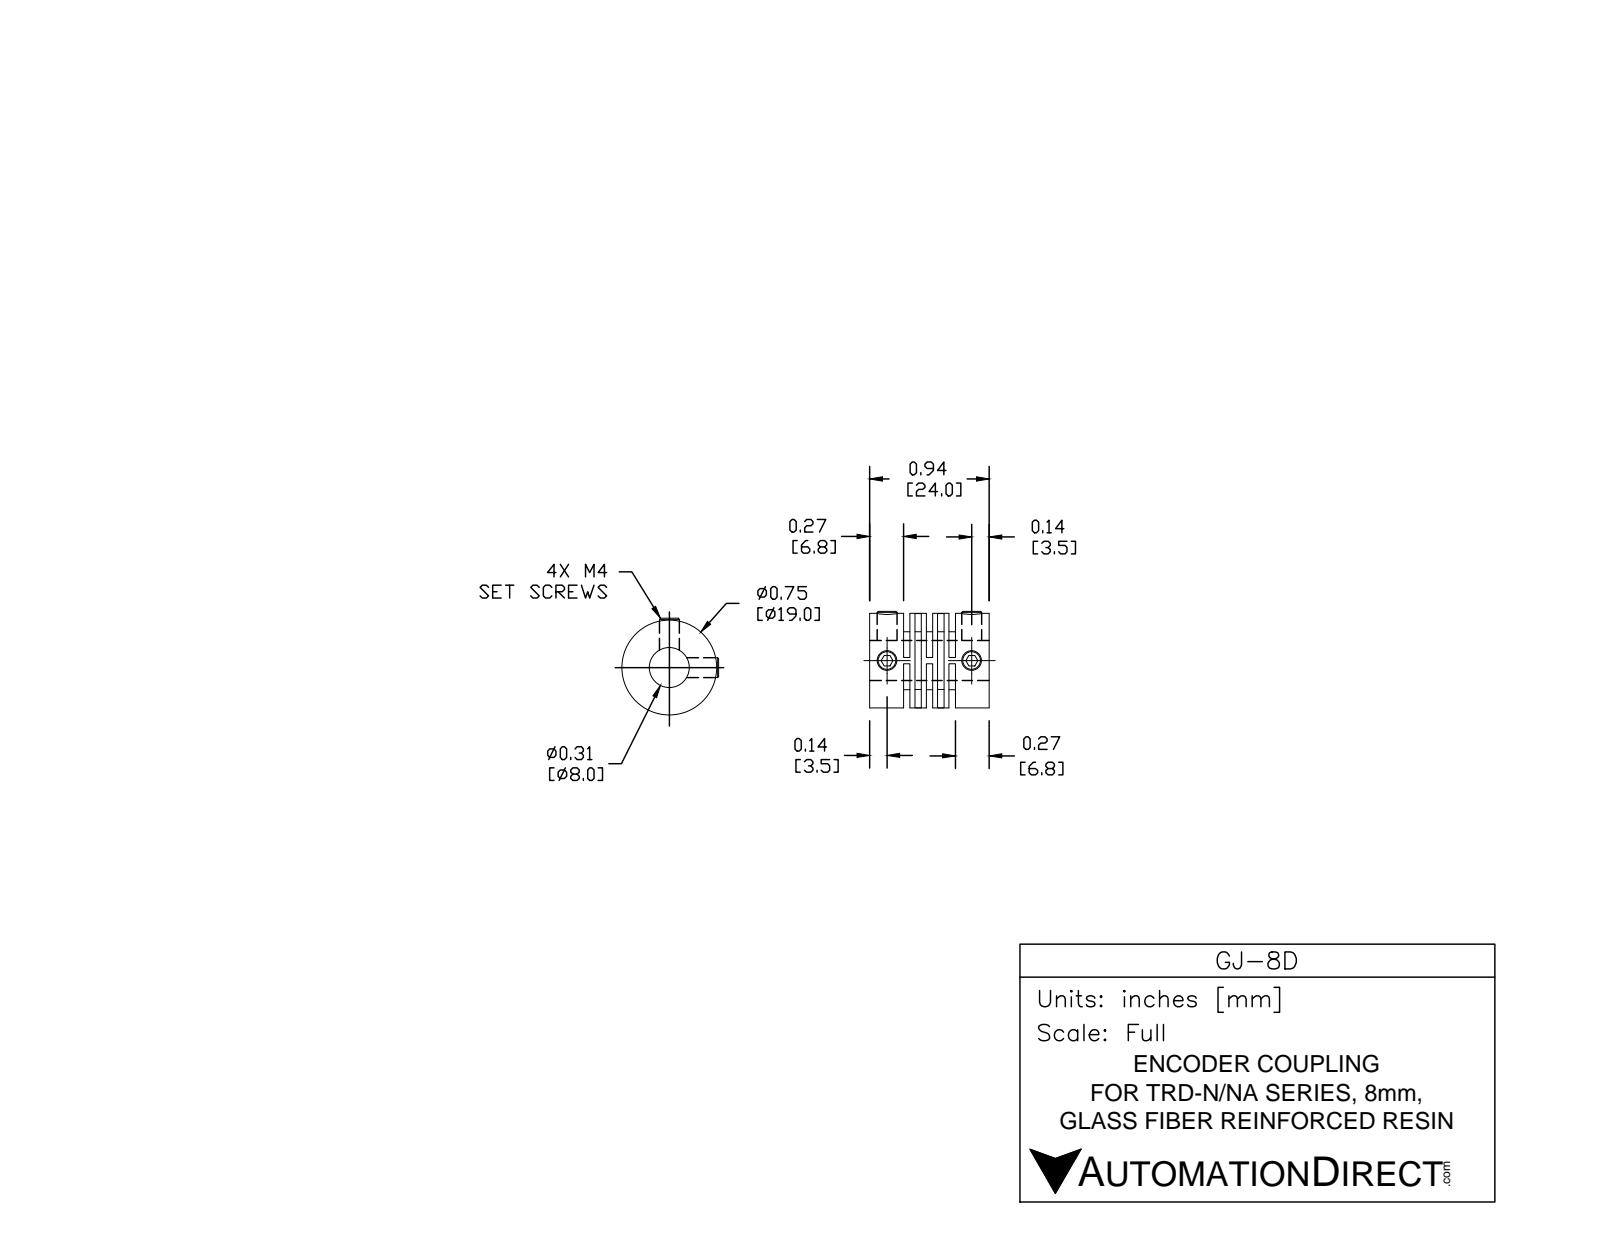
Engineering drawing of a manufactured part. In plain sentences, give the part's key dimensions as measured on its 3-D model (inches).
The part is named "GJ-8D". Its 3-D file was written by "SolidWorks 2016 (AUTOMOTIVE_DESIGN)". It is 1 solid with 130 faces: 78 planar, 20 cylindrical and 32 other. Overall it measures 0.945 by 0.748 by 0.748 inches. Its volume is 0.262 cubic inches and its surface area 6.987 square inches. Round holes: 4 of diameter 0.157, 1 of diameter 0.315. Round bosses or shafts: 1 of diameter 0.748. The main face-to-face distances are 0.047, 0.094, 0.181, 0.134, 0.228, 0.276, 0.268, 0.406, 0.539, 0.358. The hole center spacings are 0.669.
